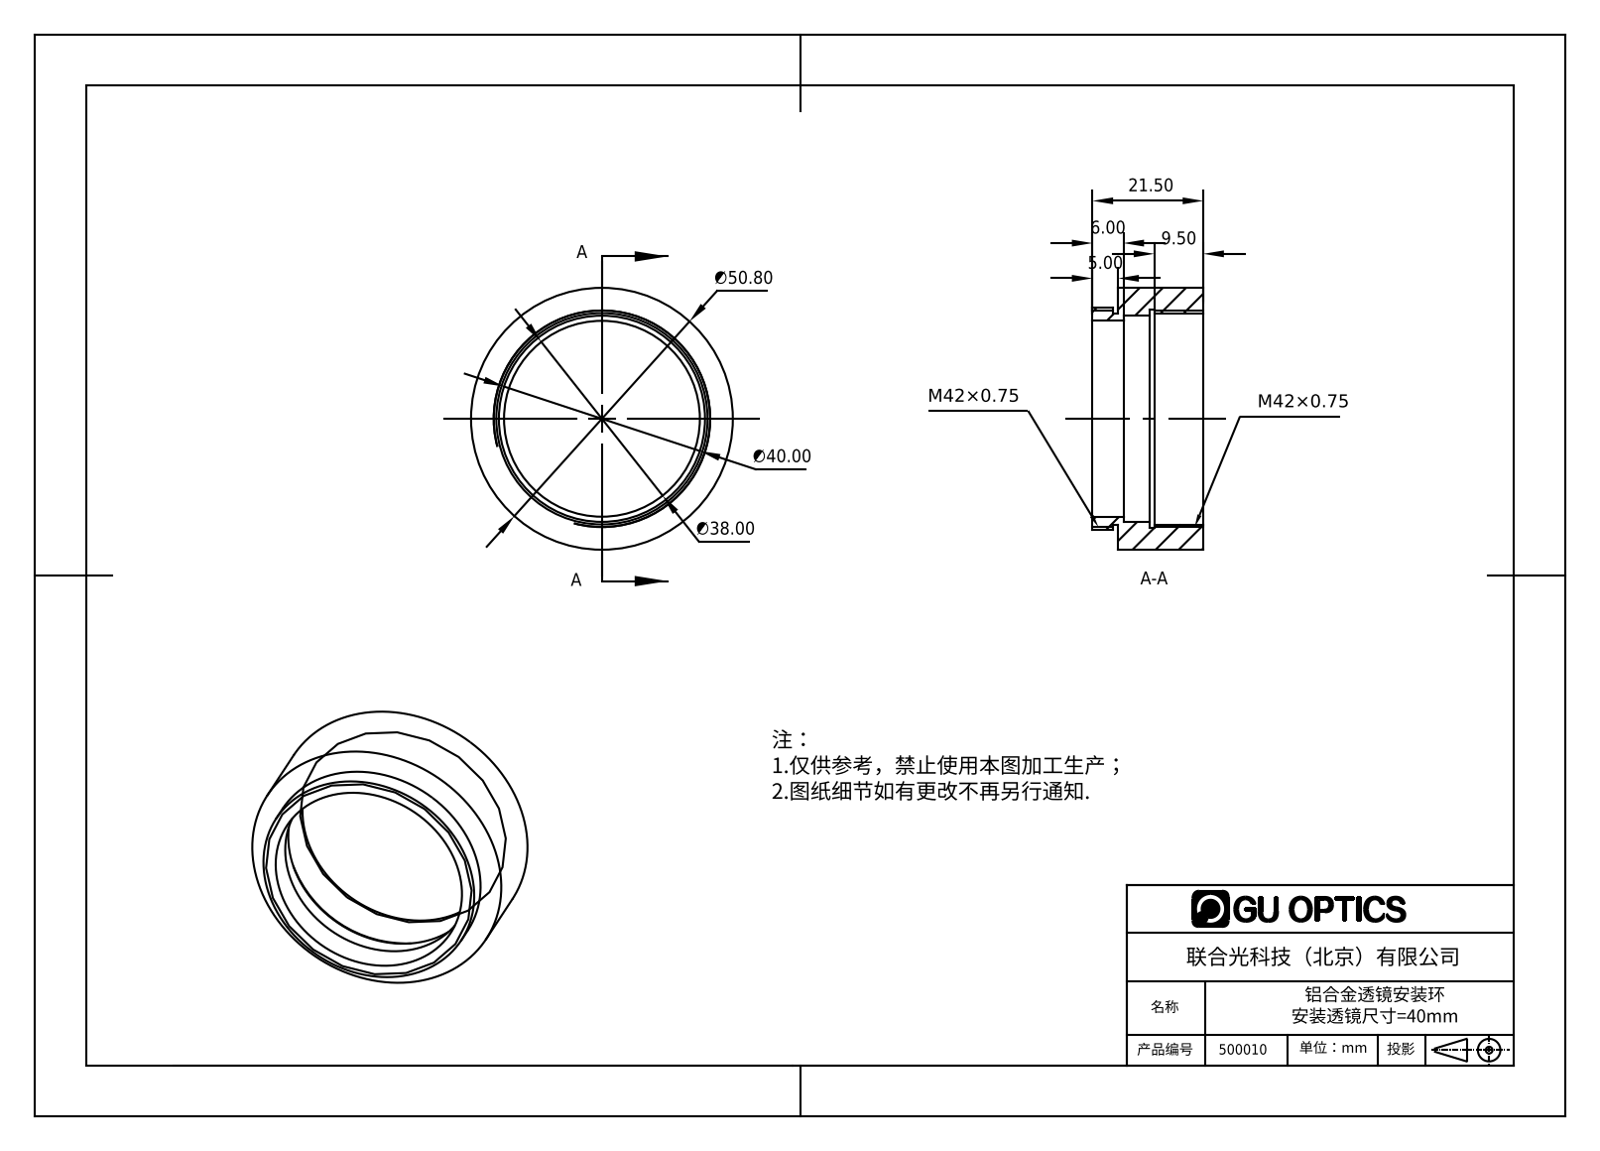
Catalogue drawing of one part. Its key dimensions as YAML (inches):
part_name: "500010"
step_written_by: "SolidWorks 2016 (AUTOMOTIVE_DESIGN)"
units: inches
bodies: {solids: 1, faces: 21, planar: 7, cylindrical: 14, other: 0}
overall_size: [2, 2, 0.846]
volume: 0.826
surface_area: 12.72
round_holes:
  - {diameter: 1.496, count: 1}
  - {diameter: 1.575, count: 1}
  - {diameter: 1.614, count: 1}
  - {diameter: 1.661, count: 1}
round_bosses_or_shafts:
  - {diameter: 2, count: 1}
  - {diameter: 1.693, count: 1}
face_to_face_distances: [0.65, 0.197, 0.236, 0.039, 0.846, 0.276, 0.433, 0.413, 0.157, 0.689]
